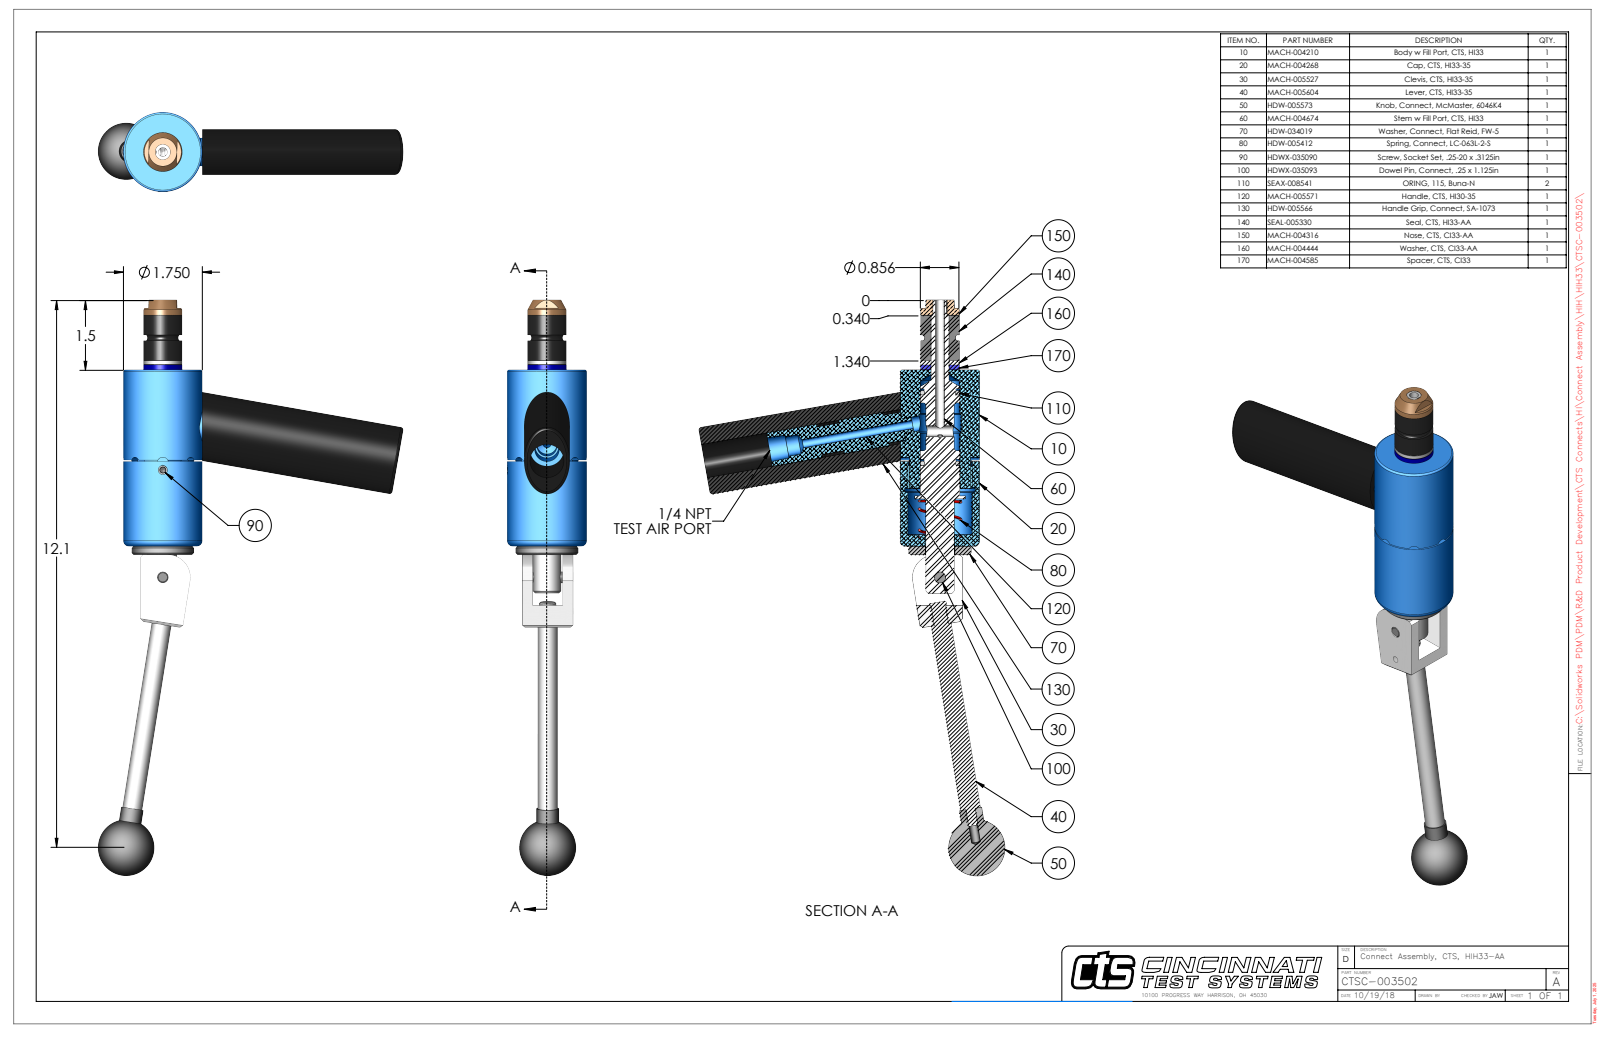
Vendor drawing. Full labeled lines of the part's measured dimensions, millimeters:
Part name (STEP PRODUCT): CTSC-003502
STEP written by: SolidWorks 2023 (AUTOMOTIVE_DESIGN)
Units: millimetres
Bodies: 11 solids, 288 faces (93 planar, 126 cylindrical, 69 other)
Overall size (bounding box): 323.9 × 171.8 × 44.5
Volume: 288 100 mm³ · Surface area: 71 230 mm²
Round holes (diameter × count): ⌀5.1 ×2, ⌀8 ×2, ⌀3.8 ×1, ⌀4.7 ×1, ⌀5.2 ×1, ⌀6.3 ×1, ⌀6.4 ×1, ⌀6.4 ×1, ⌀9.9 ×1, ⌀10.1 ×1, ⌀10.2 ×1, ⌀11.1 ×1
Round bosses / shafts (diameter × count): ⌀9.5 ×2, ⌀7.9 ×2, ⌀6.4 ×2, ⌀44.5 ×1, ⌀35.1 ×1, ⌀21.8 ×1, ⌀21.7 ×1, ⌀19.1 ×1
Partial cylindrical surfaces — rounded edges, fillets, slot ends (radius × count): R3.2 ×4, R0.7 ×2, R3.8 ×1, R8.4 ×1, R12.7 ×1, R17.7 ×1, R20.9 ×1
Main face-to-face distances: 99.2, 28.4, 104, 4.8, 22.6, 5.9, 5.9, 16.7, 22.6, 30.7
Hole centre spacings: 18.8, 60.4, 79.1
